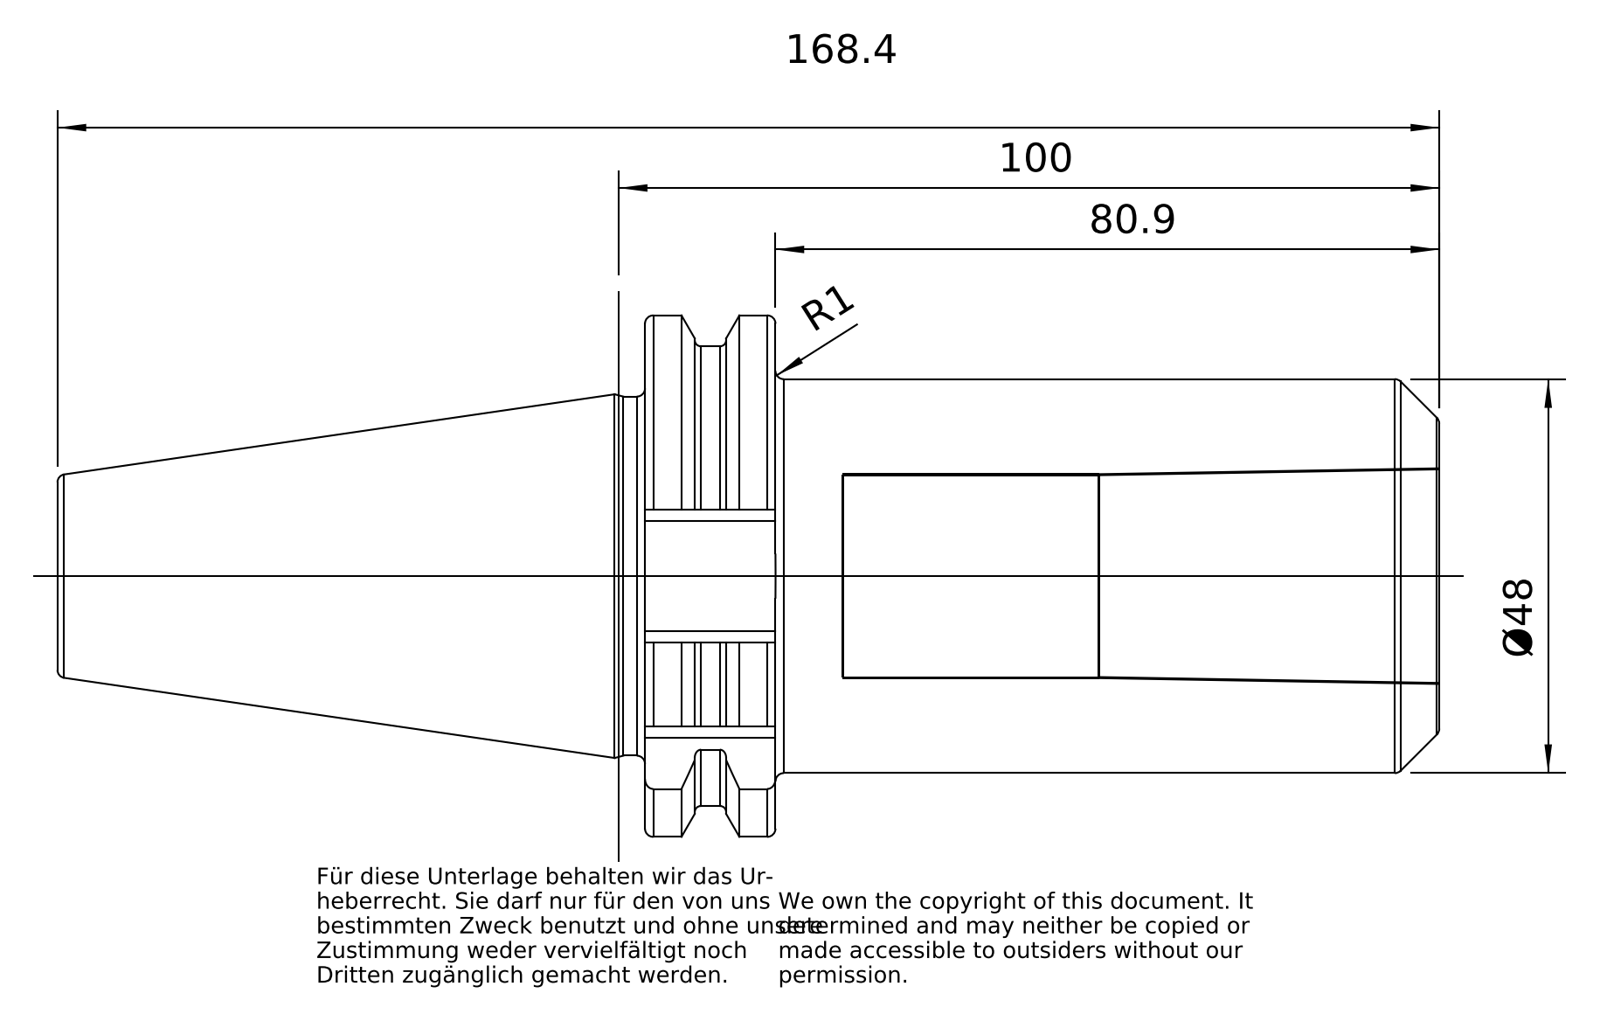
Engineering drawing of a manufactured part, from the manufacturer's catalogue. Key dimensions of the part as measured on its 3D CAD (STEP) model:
Part name (STEP PRODUCT): 40-421-03
STEP written by: PRO/ENGINEER BY PARAMETRIC TECHNOLOGY CORPORATION, 2010430 (CONFIG_CONTROL_DESIGN)
Units: millimetres
Bodies: 1 solid, 102 faces (23 planar, 28 cylindrical, 51 other)
Overall size (bounding box): 168.25 × 63.52 × 61.42
Volume: 214 440 mm³ · Surface area: 37 310 mm²
Round holes (diameter × count): ⌀13.84 ×1, ⌀17.01 ×1, ⌀17.5 ×1, ⌀24.72 ×1
Round bosses / shafts (diameter × count): ⌀48 ×1, ⌀43.75 ×1, ⌀16.01 ×1
Partial cylindrical surfaces — rounded edges, fillets, slot ends (radius × count): R1.35 ×5, R28 ×1, R31.76 ×1
Main face-to-face distances: 15.85, 96.8, 80.95, 24.1, 8.25, 72.7, 47.4, 16.2, 71.45, 87.3
